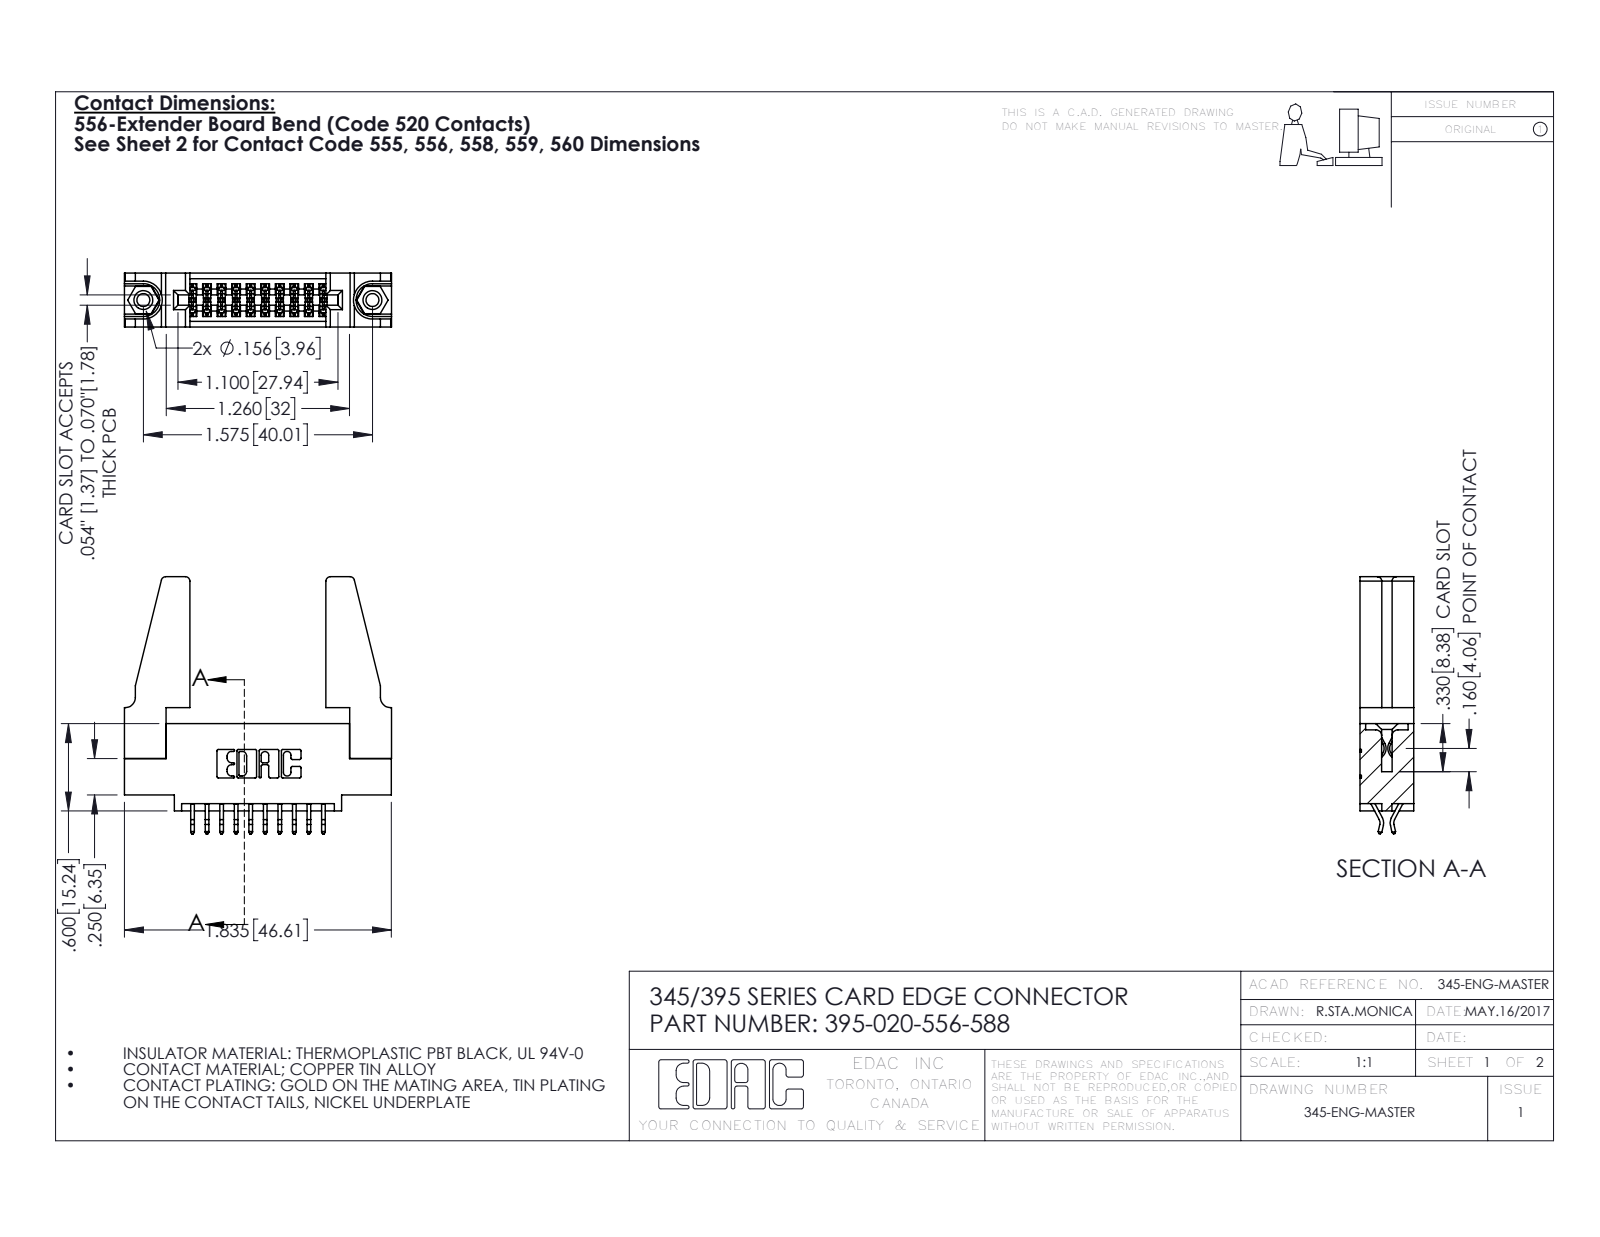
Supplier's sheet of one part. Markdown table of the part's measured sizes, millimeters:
| quantity | value |
| --- | --- |
| part name | 345 Part_0.110 Offset - 0.156 Dia-TH; 345-292-001_556 Tail; 345-250-001_345-250-001-102; 395-020-556-588 (+1 more) |
| STEP written by | SolidWorks 2016 (CONFIG_CONTROL_DESIGN) |
| units | millimeters |
| bodies | 25 solids, 1374 faces (896 planar, 462 cylindrical, 16 other) |
| overall size | 46.6 × 44.9 × 9.4 |
| volume | 7 410 mm³ |
| surface area | 8 723 mm² |
| round holes (diameter × count) | 2.3 × 2, 3.2 × 2, 4 × 2, 1.6 × 1 |
| round bosses / shafts (diameter × count) | 3.9 × 2 |
| partial cylindrical surfaces (radius × count) | 0.2 × 30, 0.3 × 22, 0.8 × 8, 0.2 × 6, 0.8 × 6, 0.7 × 3, 0.3 × 2, 0.4 × 2 |
| main face-to-face distances | 9.4, 1.8, 7.6, 5.1, 0.6, 2.5, 6.9, 5.7, 3.8, 3.8 |
| hole center spacings | 6.9, 34.1, 40 |
